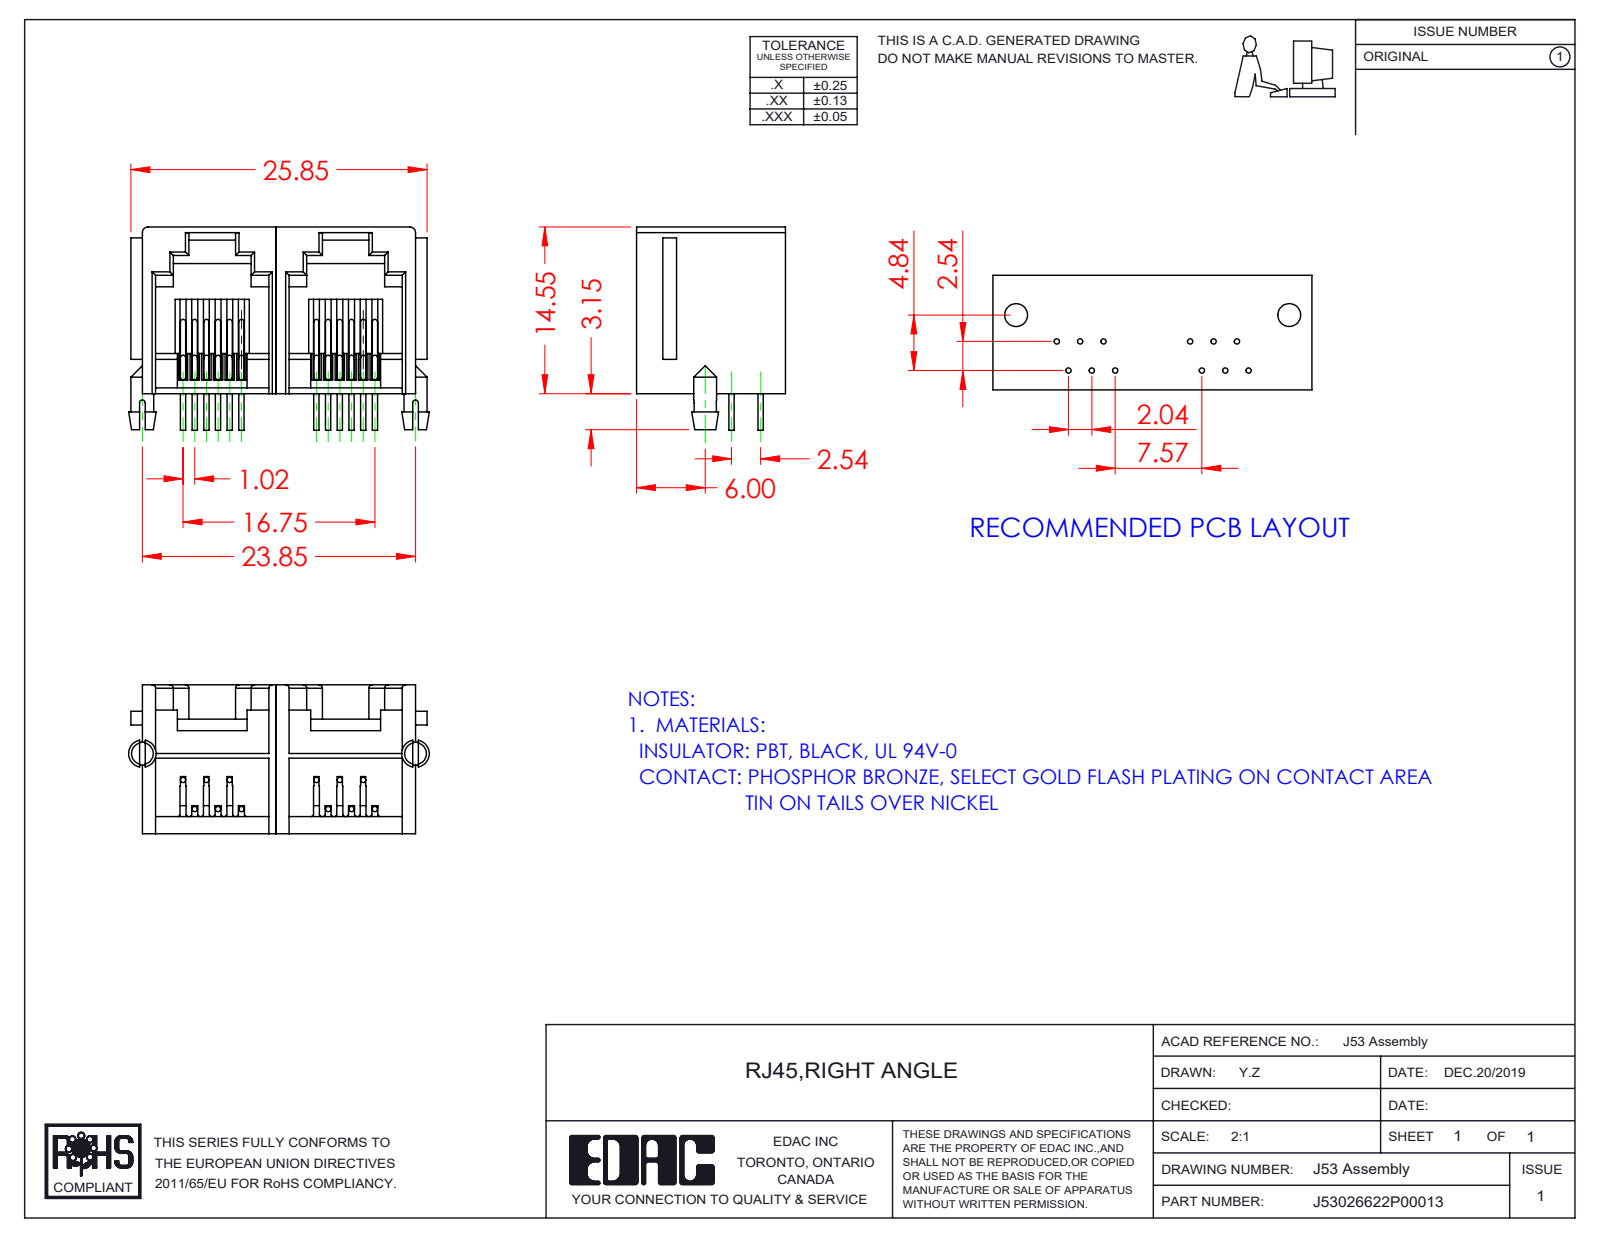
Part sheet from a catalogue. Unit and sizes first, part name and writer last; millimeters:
Units: millimetres
Overall size (bounding box): 26.25 × 17.75 × 13
Round bosses / shafts (diameter × count): ⌀0.46 ×36, ⌀2 ×2
Partial cylindrical surfaces — rounded edges, fillets, slot ends (radius × count): R0.3 ×14, R0.5 ×10, R0.25 ×2, R0.67 ×1
Main face-to-face distances: 11.65, 1.16, 11.04, 12.2, 22.69, 10.49, 12.81, 0.61, 9.88, 3
Volume: 1 800 mm³ · Surface area: 4 280 mm²
Bodies: 14 solids, 595 faces (410 planar, 128 cylindrical, 57 other)
Part name (STEP PRODUCT): 53 Contact - 4; 53 Contact - 1; 53 Contact - 6; 53 Insulator RH (+6 more)
STEP written by: SolidWorks 2016 (CONFIG_CONTROL_DESIGN)
